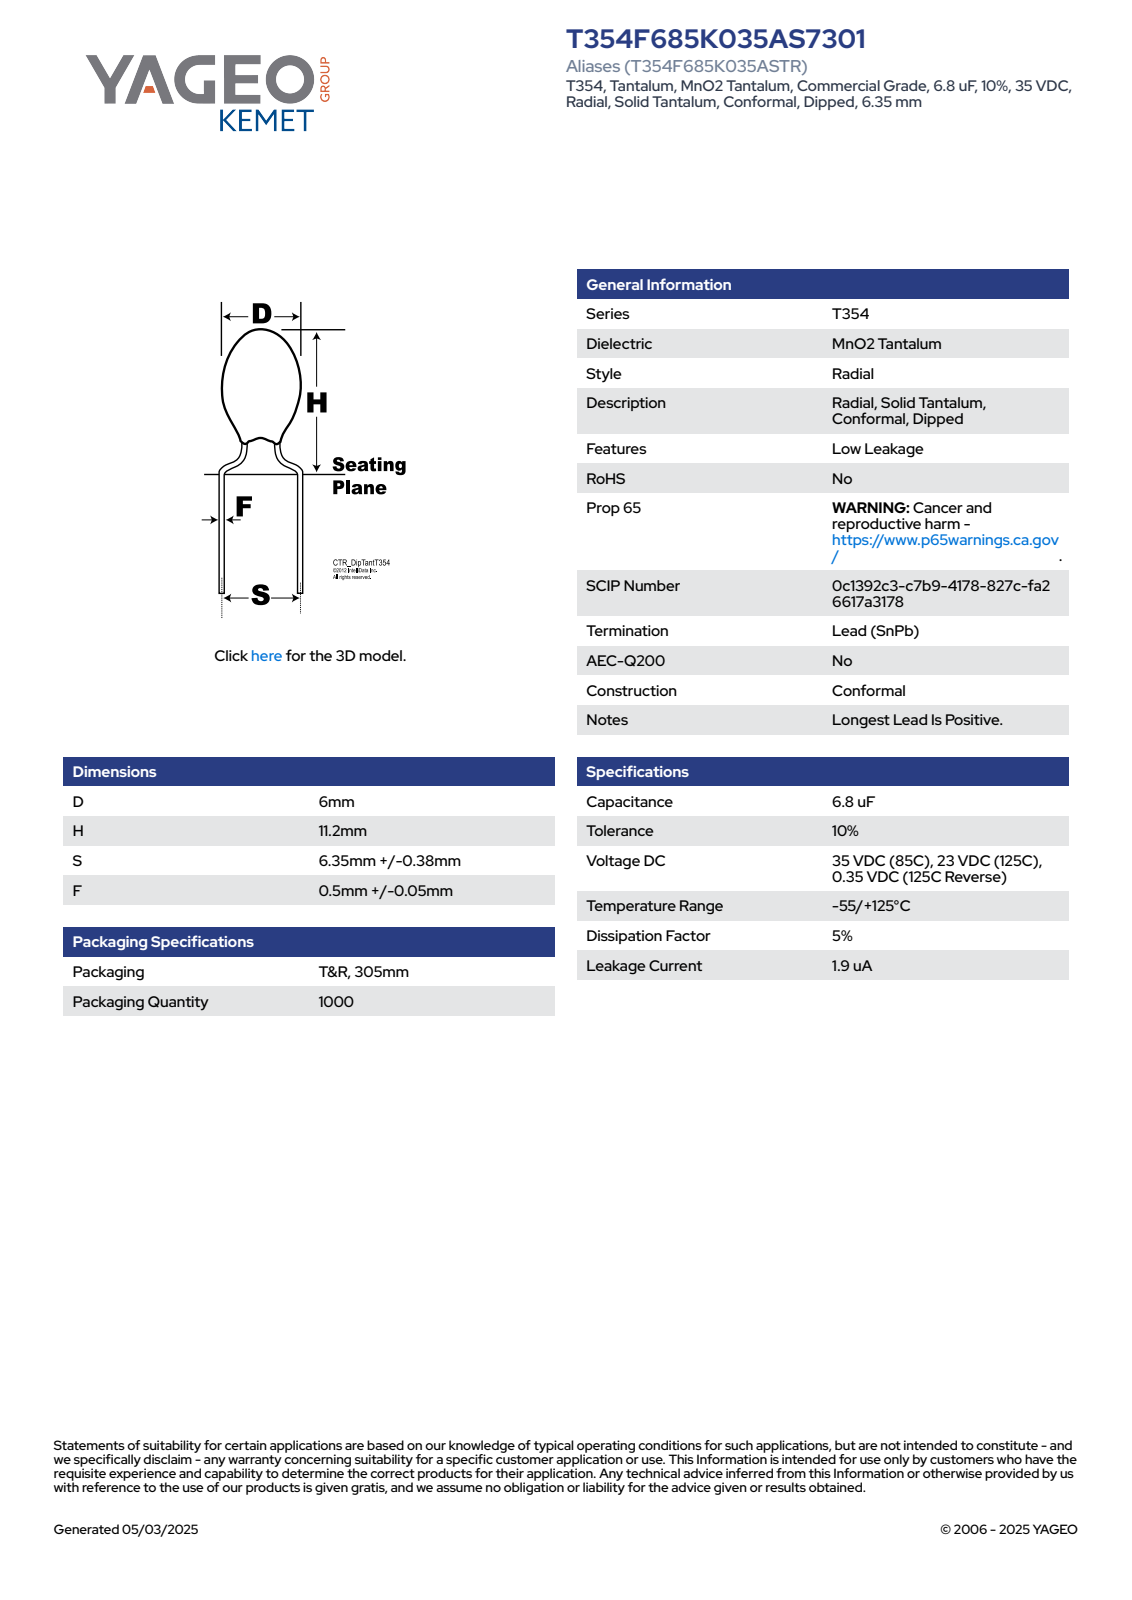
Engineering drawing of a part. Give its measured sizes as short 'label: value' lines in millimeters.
name: CTR_T354_D6H11.2S6.35LL5.56F0.55
written by: SolidWorks 2014 (AUTOMOTIVE_DESIGN)
unit: mm
bodies: 1 solid, 83 faces (28 planar, 10 cylindrical, 45 other)
size: 16.76 × 6.9 × 6
volume: 198 mm³; area: 204 mm²
bosses: 2× ⌀0.55, 1× ⌀6
rounds: 1× R2.99
face distances: 7.81, 8.95, 16.76, 14, 5.05, 2.76, 13.2, 4.25, 0.8, 3.56
